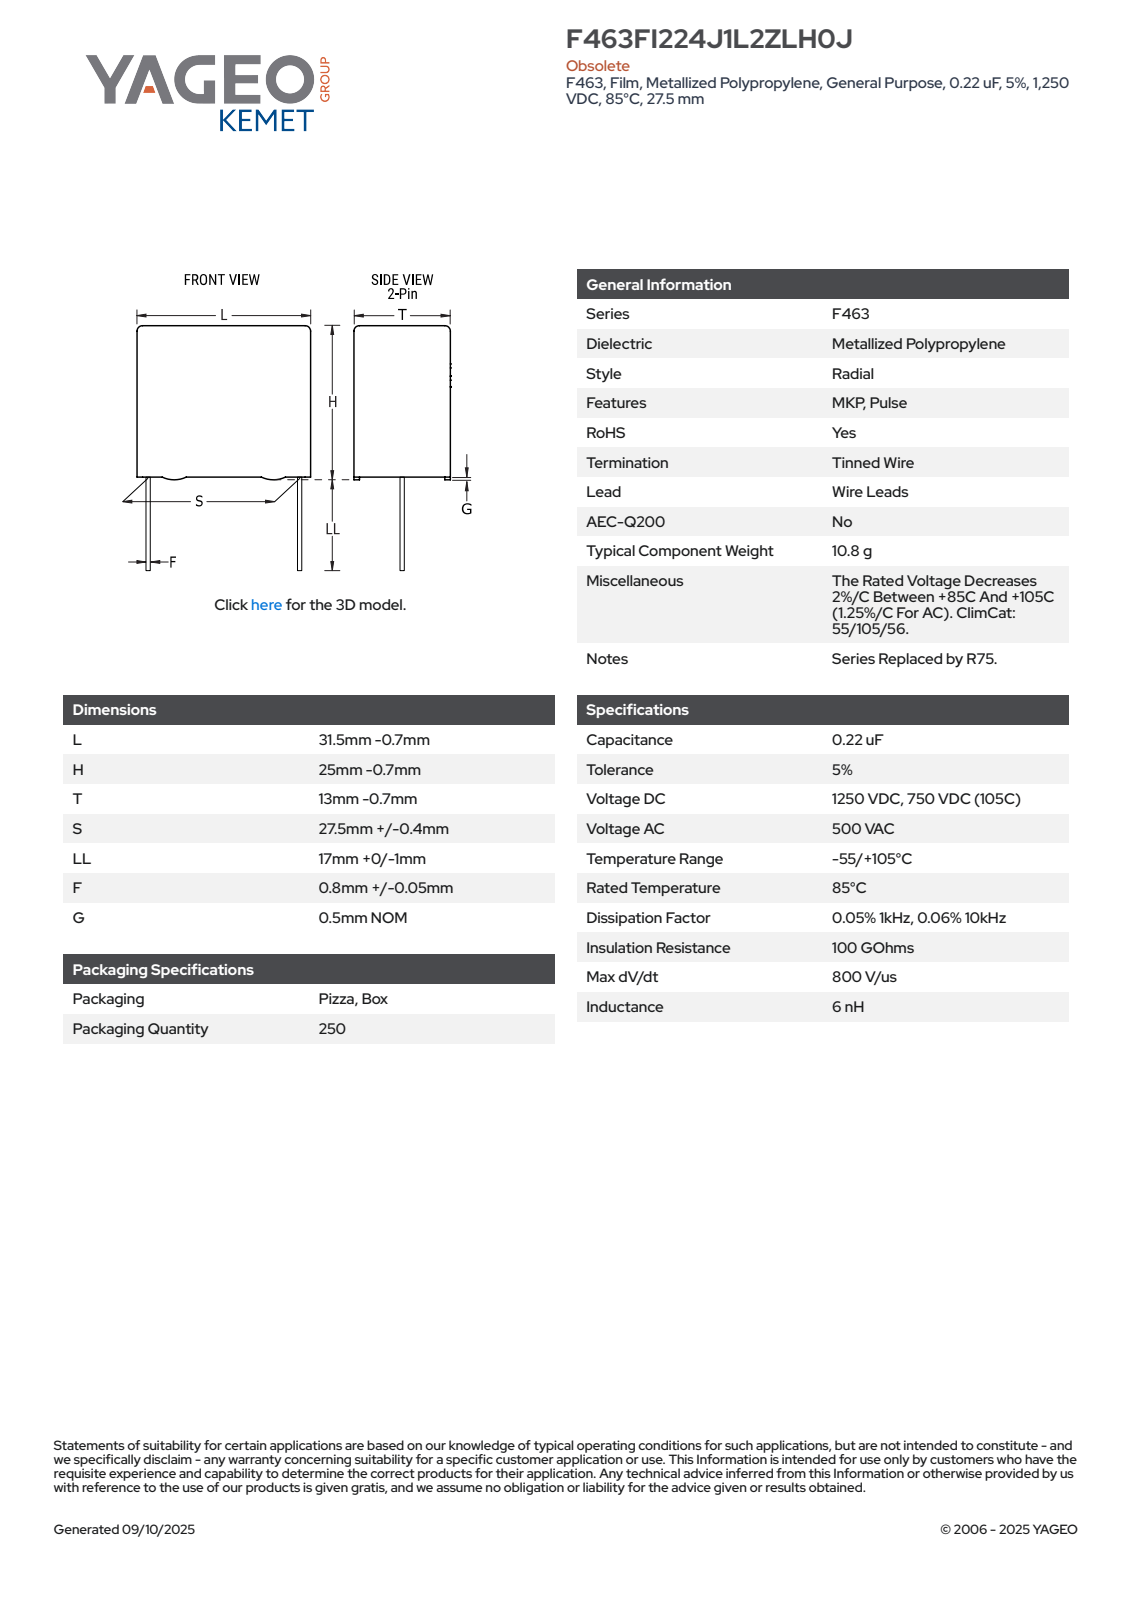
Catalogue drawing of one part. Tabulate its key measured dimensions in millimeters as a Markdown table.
| quantity | value |
| --- | --- |
| part name | CFR_RBG_31.5X25X13_L30.8H24.3T12.3S27.5LL17F0.85G0.5 |
| STEP written by | SolidWorks 2014 (AUTOMOTIVE_DESIGN) |
| units | millimeters |
| bodies | 4 solids, 89 faces (81 planar, 8 cylindrical, 0 other) |
| overall size | 41.3 × 30.8 × 12.3 |
| volume | 9 039 mm³ |
| surface area | 3 008 mm² |
| round bosses / shafts (diameter × count) | 0.85 × 2 |
| partial cylindrical surfaces (radius × count) | 0.5 × 4 |
| main face-to-face distances | 12.3, 23.8, 30.8, 0.5, 24.3, 0.7, 11.6, 10.9, 17, 17.5 |
